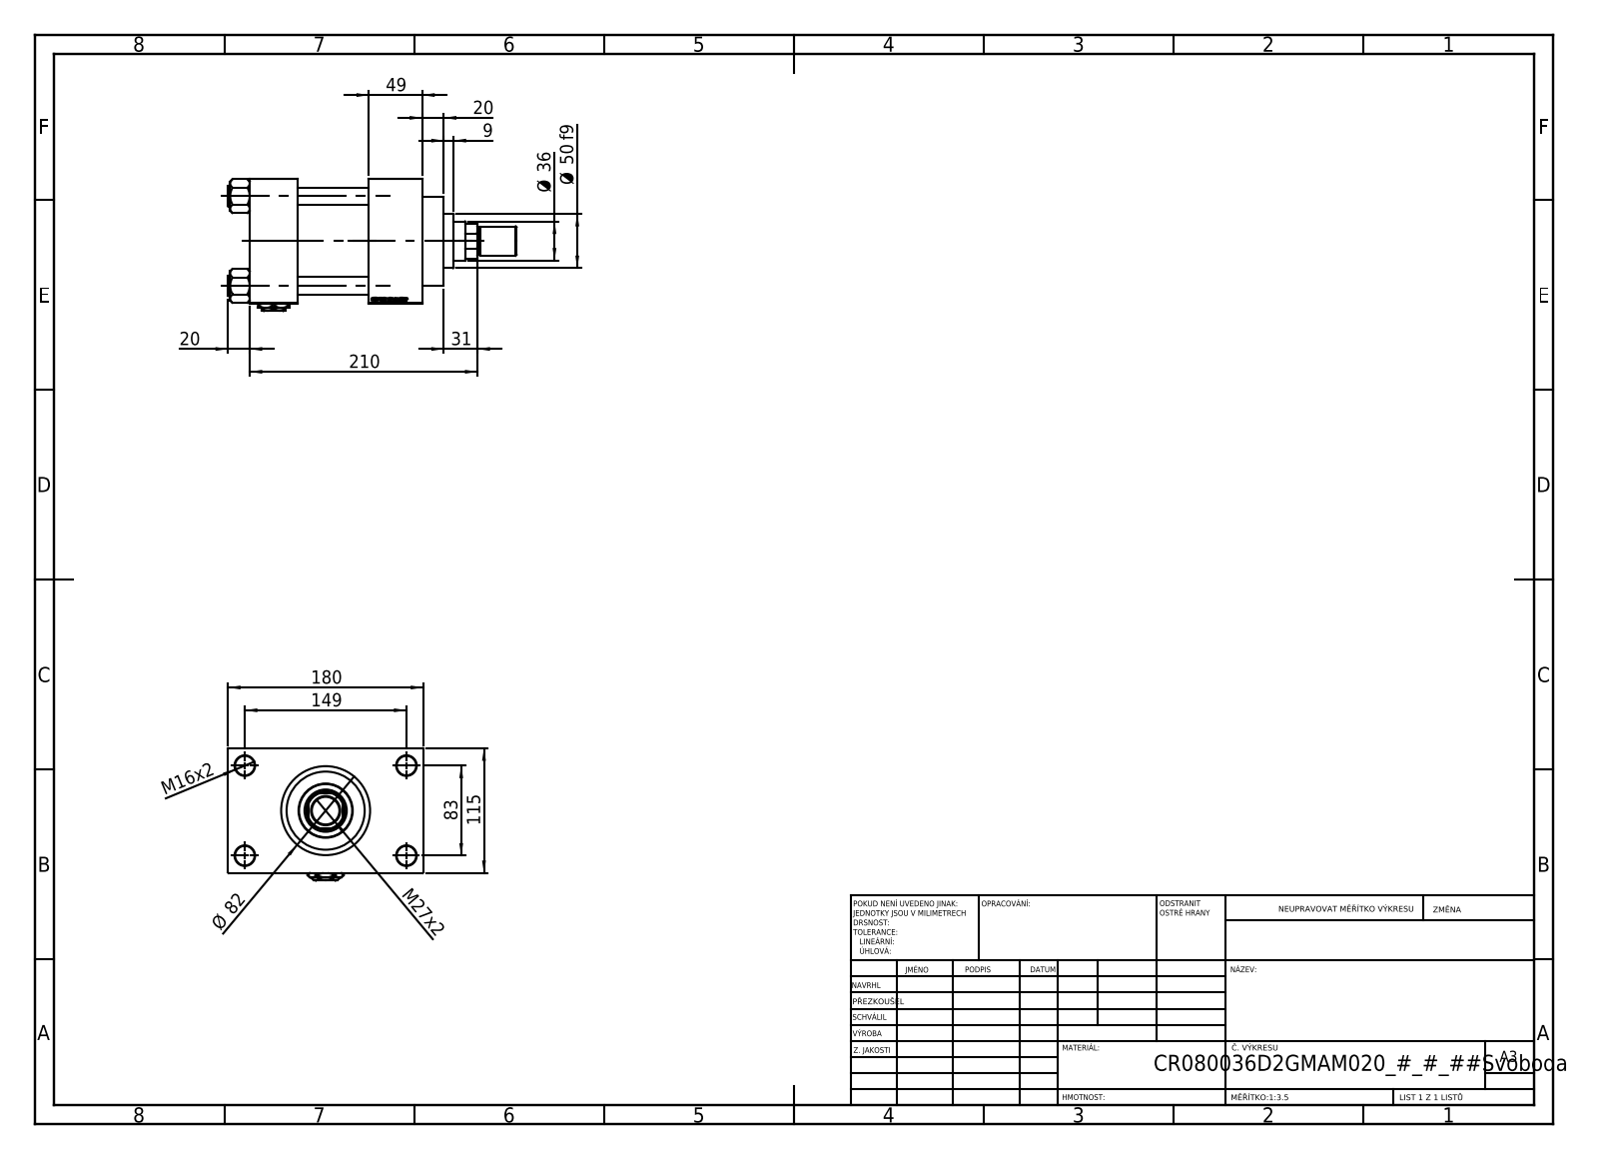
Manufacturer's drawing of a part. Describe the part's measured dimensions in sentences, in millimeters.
The part is named "ROD_END_AH; V215CR_D_Body; V215CR_VCP_D; V215CR_D_TYCINKA (+3 more)". Its 3-D file was written by "SolidWorks 2019 (CONFIG_CONTROL_DESIGN)". It is 13 solids with 1218 faces: 573 planar, 99 cylindrical and 546 other. Overall it measures 266 by 180 by 122 millimeters. Its volume is 1 997 000 cubic millimeters and its surface area 304 500 square millimeters. Round holes: 4 of diameter 16, 4 of diameter 18, 3 of diameter 7, 3 of diameter 26.44, 3 of diameter 35, 1 of diameter 25.5, 1 of diameter 36, 1 of diameter 39, 1 of diameter 61, 1 of diameter 72, 1 of diameter 80. Round bosses or shafts: 4 of diameter 19, 1 of diameter 86, 1 of diameter 82, 1 of diameter 50, 1 of diameter 27, 1 of diameter 25. Partial cylindrical surfaces (rounded edges, fillets, slot ends): 1 of radius 17.5. The main face-to-face distances are 115, 66, 110, 49, 44, 159, 32.5, 147.5, 20, 69. The hole center spacings are 33.15, 58.48, 82.7, 85.28, 89.24, 115.85, 142.43, 83.
